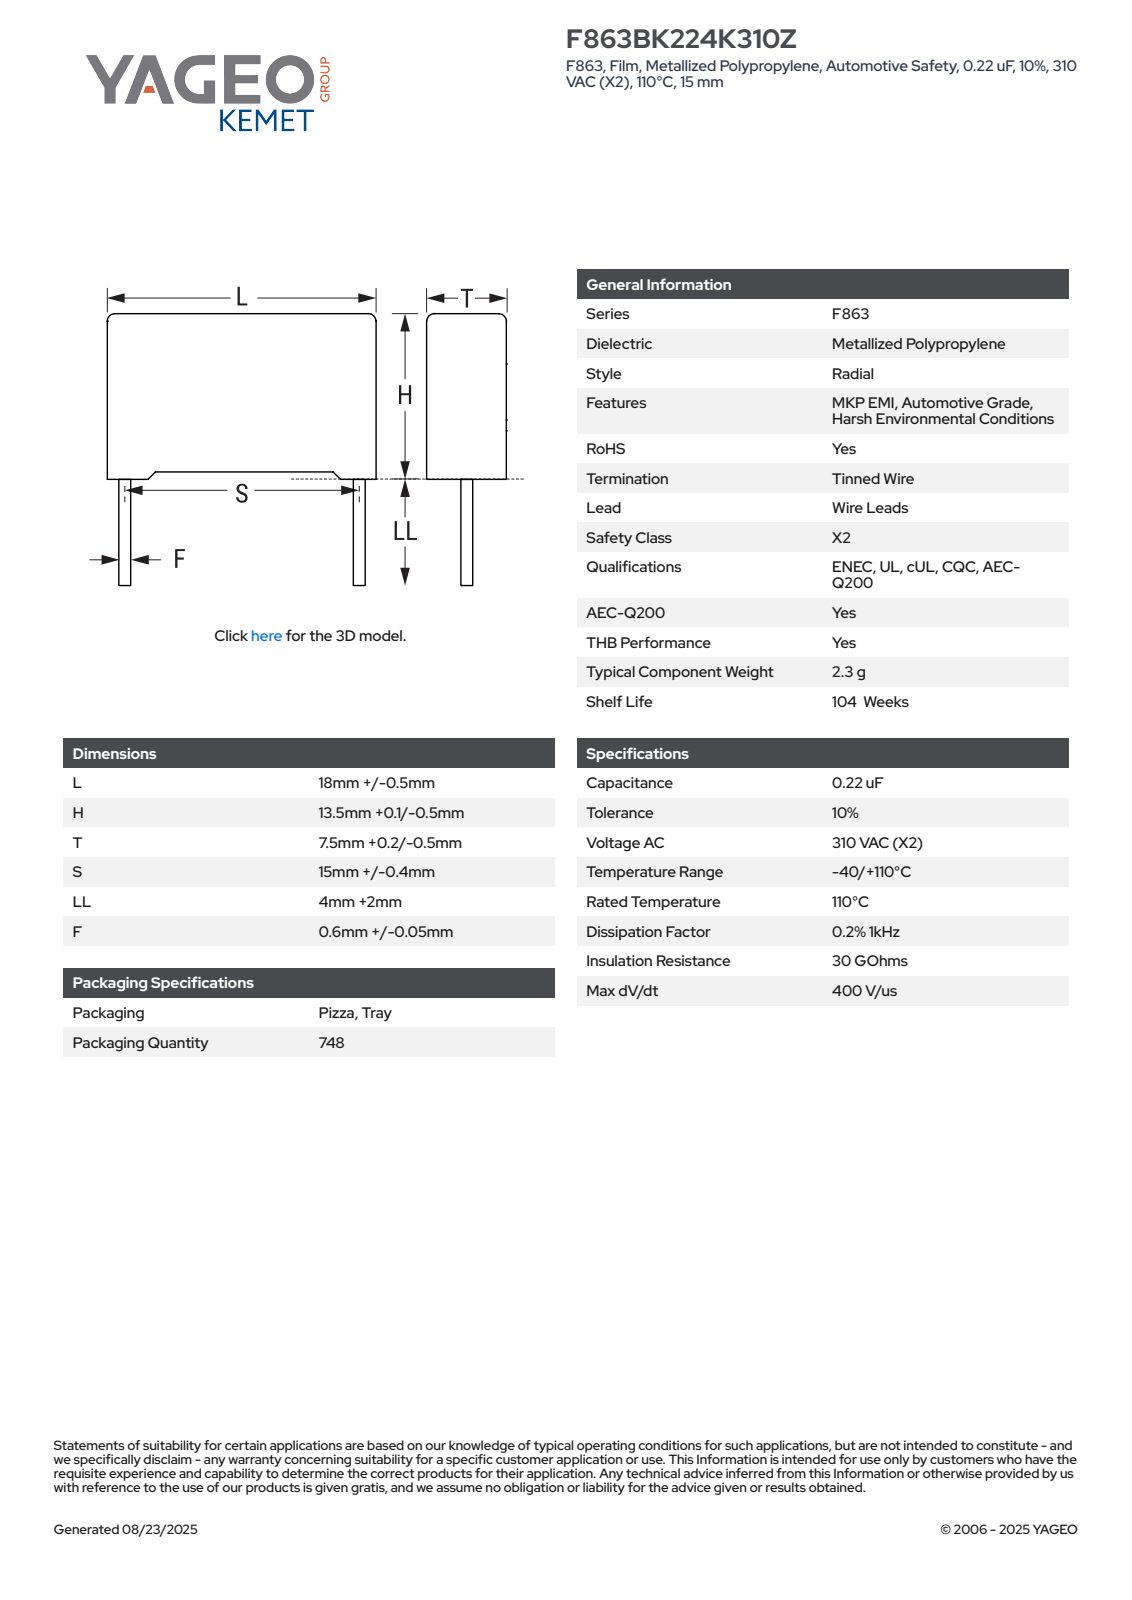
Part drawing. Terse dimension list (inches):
name: CFR_RB_18X13.5X7.5_L18.3H13.6T7.7S15LL6F0.65
written by: SolidWorks 2014 (AUTOMOTIVE_DESIGN)
unit: in
bodies: 4 solids, 89 faces (81 planar, 8 cylindrical, 0 other)
size: 0.772 × 0.72 × 0.304
volume: 0.112 in³; area: 1.569 in²
bosses: 2× ⌀0.026
rounds: 4× R0.019
face distances: 0.303, 0.511, 0.72, 0.304, 0.024, 0.024, 0.28, 0.535, 0.256, 0.28
